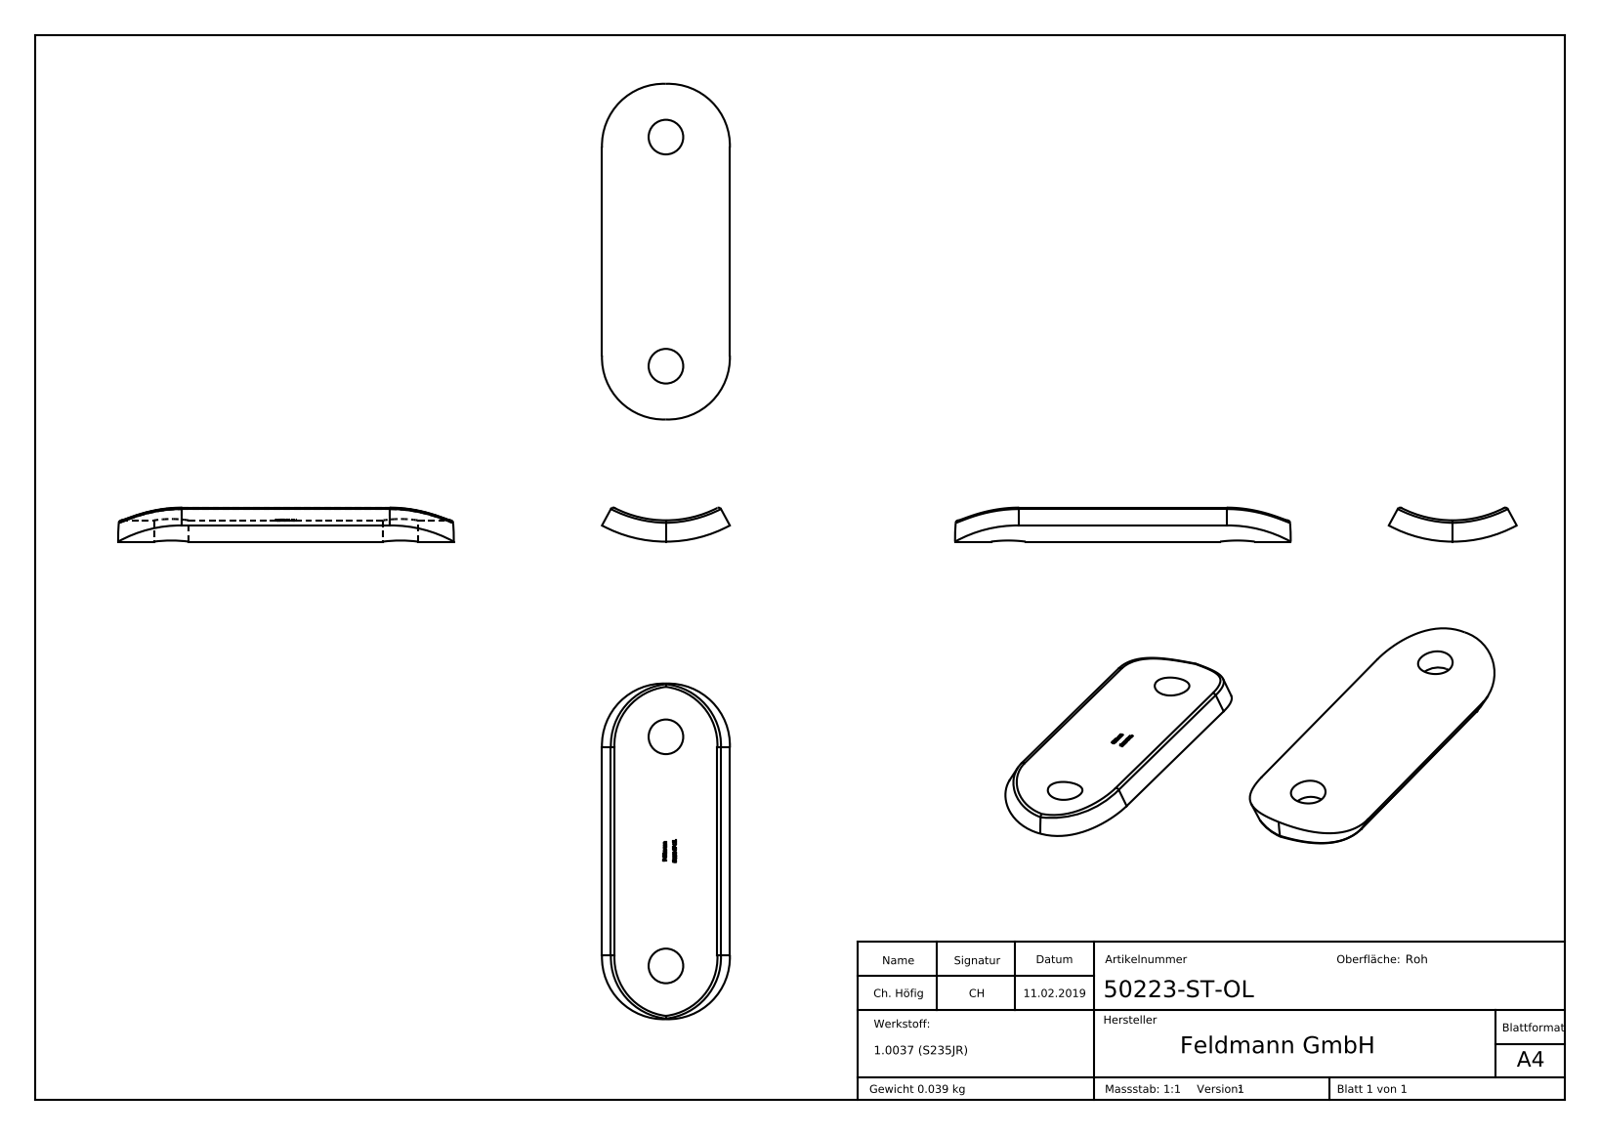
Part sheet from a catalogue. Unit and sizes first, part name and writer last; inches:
Units: inches
Overall size (bounding box): 2.48 × 0.945 × 0.251
Round holes (diameter × count): ⌀0.256 ×2
Partial cylindrical surfaces — rounded edges, fillets, slot ends (radius × count): R0.472 ×4, R0.02 ×2, R0.835 ×1, R0.992 ×1
Main face-to-face distances: 0.047, 0.045, 0.073, 0.063, 0.075, 0.021, 0.026, 0.019, 0.043, 0.065
Hole centre spacings: 1.693
Volume: 0.307 in³ · Surface area: 5.062 in²
Bodies: 1 solid, 255 faces (120 planar, 17 cylindrical, 118 other)
Part name (STEP PRODUCT): 50223-ST-OL
STEP written by: SolidWorks 2015 (CONFIG_CONTROL_DESIGN)
